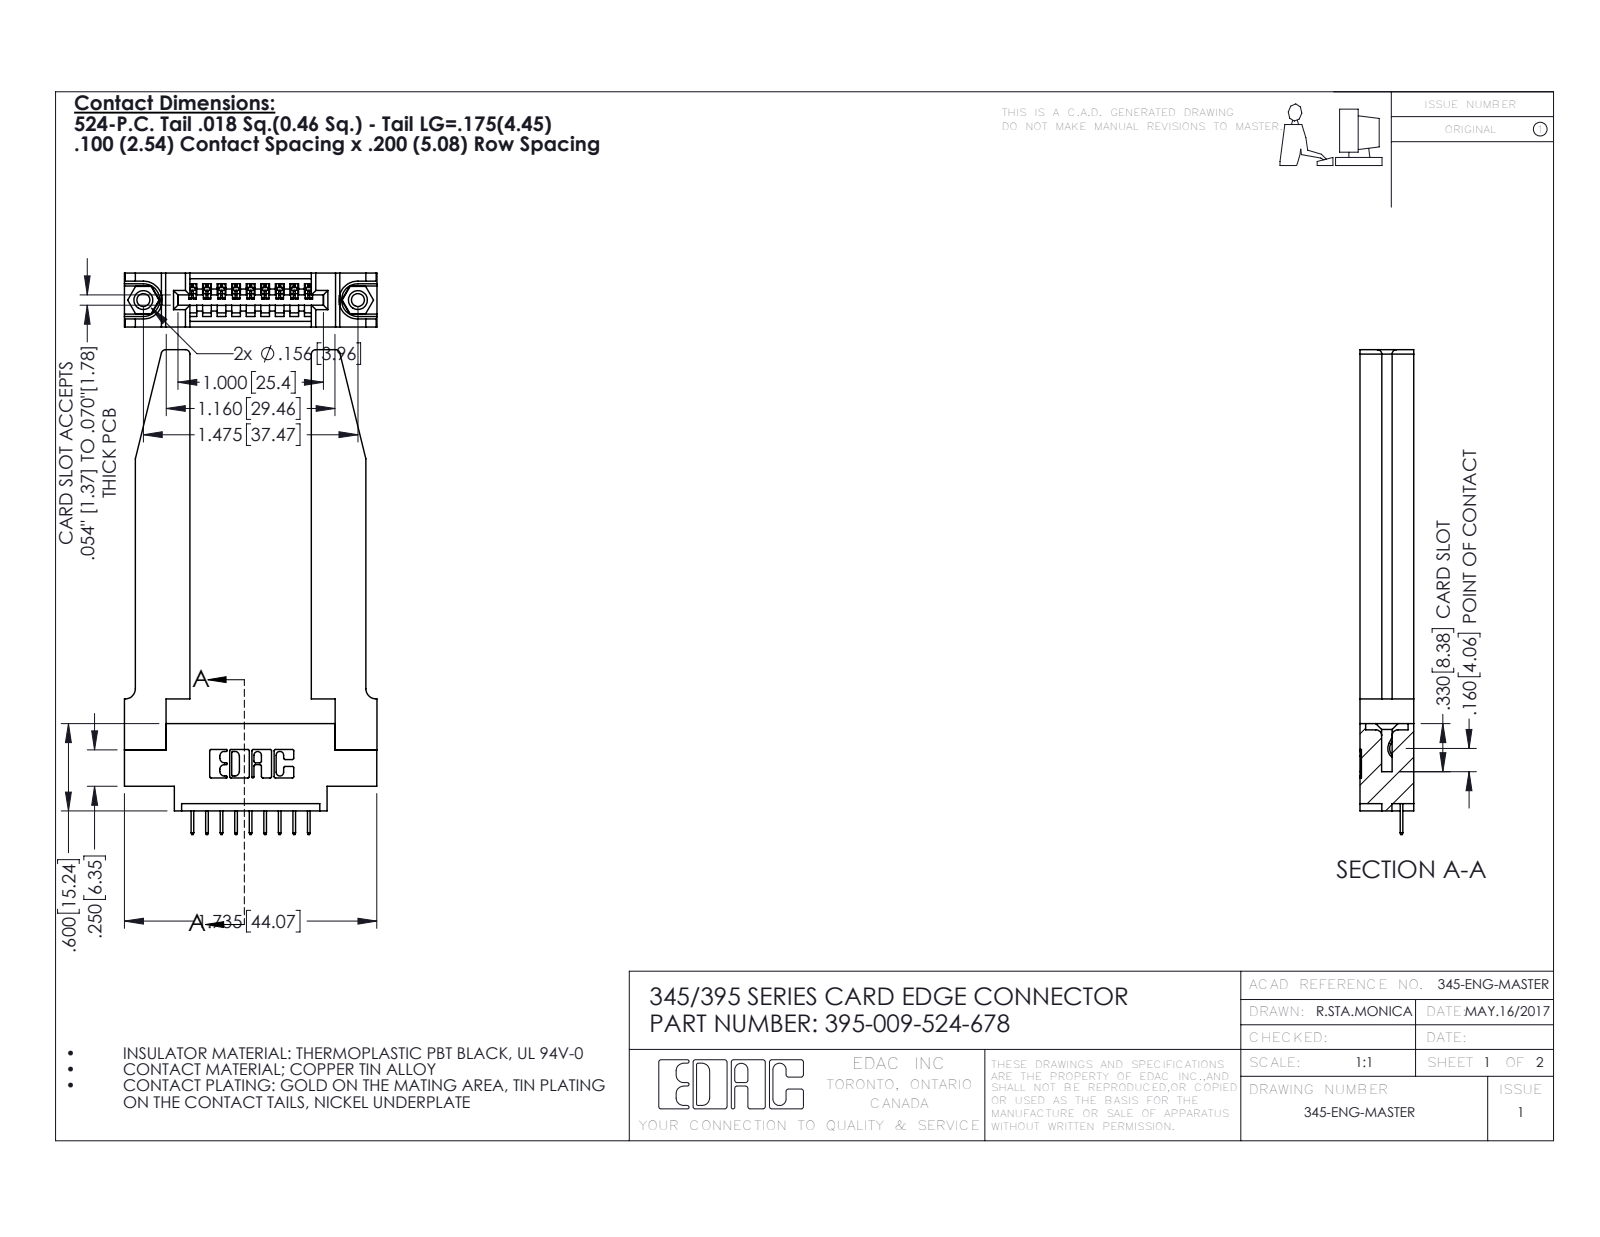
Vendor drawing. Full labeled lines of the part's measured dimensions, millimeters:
Part name (STEP PRODUCT): 345-250-001_345-250-001-102; 345-292-001_345-293-124; 395-009-524-678; 345 Part_0.170 Offset - 0.156 Dia-TH (+1 more)
STEP written by: SolidWorks 2016 (CONFIG_CONTROL_DESIGN)
Units: millimetres
Bodies: 14 solids, 922 faces (640 planar, 230 cylindrical, 52 other)
Overall size (bounding box): 84.6 × 44.1 × 9.4
Volume: 11 500 mm³ · Surface area: 11 420 mm²
Round holes (diameter × count): ⌀2.3 ×2, ⌀3.2 ×2, ⌀4 ×2, ⌀1.6 ×1
Round bosses / shafts (diameter × count): ⌀3.9 ×2
Partial cylindrical surfaces — rounded edges, fillets, slot ends (radius × count): R0.3 ×22, R0.2 ×18, R0.8 ×8, R0.2 ×6, R0.8 ×6, R0.7 ×3, R0.8 ×2, R1 ×2
Main face-to-face distances: 9.4, 3.8, 1.8, 3.8, 5.6, 7.6, 2, 21.2, 2.4, 1.8
Hole centre spacings: 6.9, 31.6, 37.5
